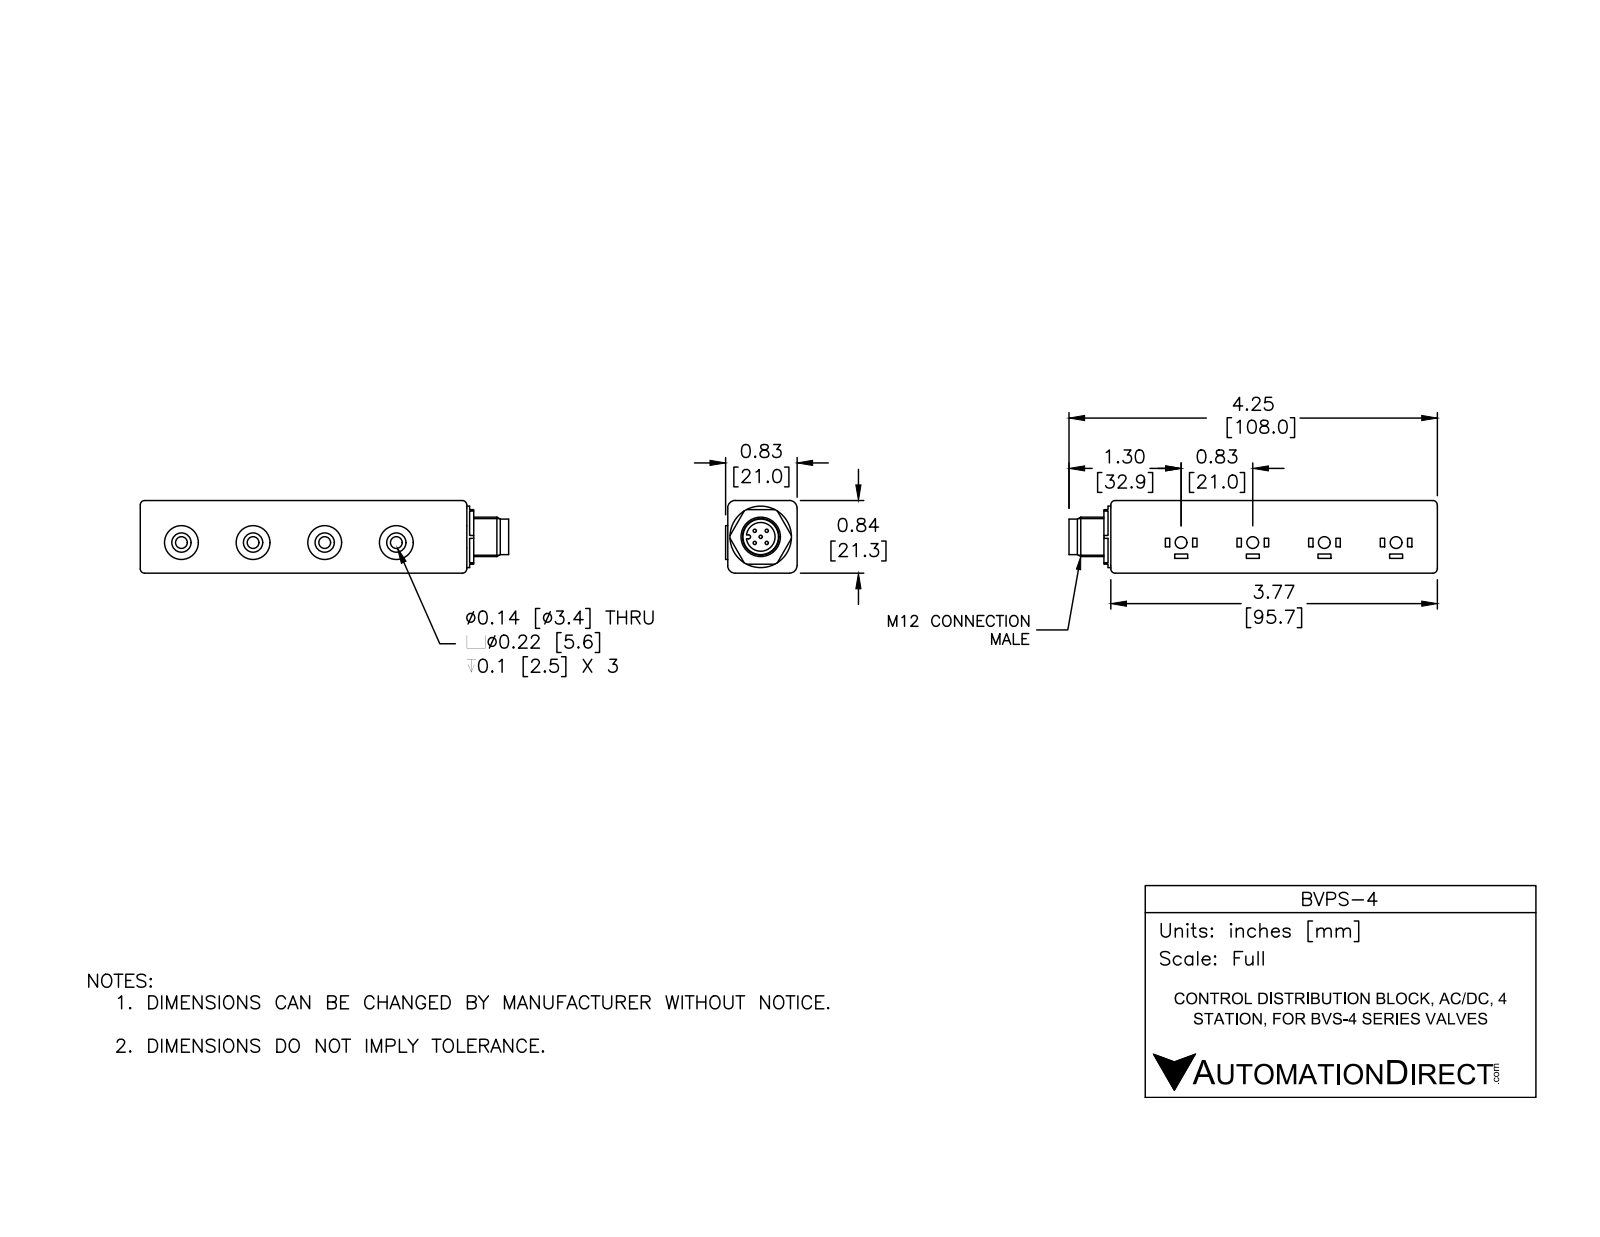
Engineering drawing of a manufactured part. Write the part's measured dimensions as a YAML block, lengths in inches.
part_name: "BVPS-4"
step_written_by: "SolidWorks 2016 (AUTOMOTIVE_DESIGN)"
units: inches
bodies: {solids: 1, faces: 163, planar: 97, cylindrical: 56, other: 10}
overall_size: [4.252, 0.839, 0.825]
volume: 2.502
surface_area: 16.78
round_holes:
  - {diameter: 0.222, count: 4}
  - {diameter: 0.135, count: 3}
  - {diameter: 0.135, count: 1}
  - {diameter: 0.331, count: 1}
round_bosses_or_shafts:
  - {diameter: 0.039, count: 5}
  - {diameter: 0.391, count: 4}
  - {diameter: 0.709, count: 1}
  - {diameter: 0.455, count: 1}
  - {diameter: 0.41, count: 1}
partial_cylinders:
  - {radius: 0.05, count: 8}
  - {radius: 0.087, count: 4}
  - {radius: 0.023, count: 1}
face_to_face_distances: [0.839, 0.8, 0.025, 0.825, 0.05, 3.849, 0.1, 0.172, 0.222, 0.667]
hole_center_spacings: [0.827, 0.827, 1.654, 1.654, 2.481]
